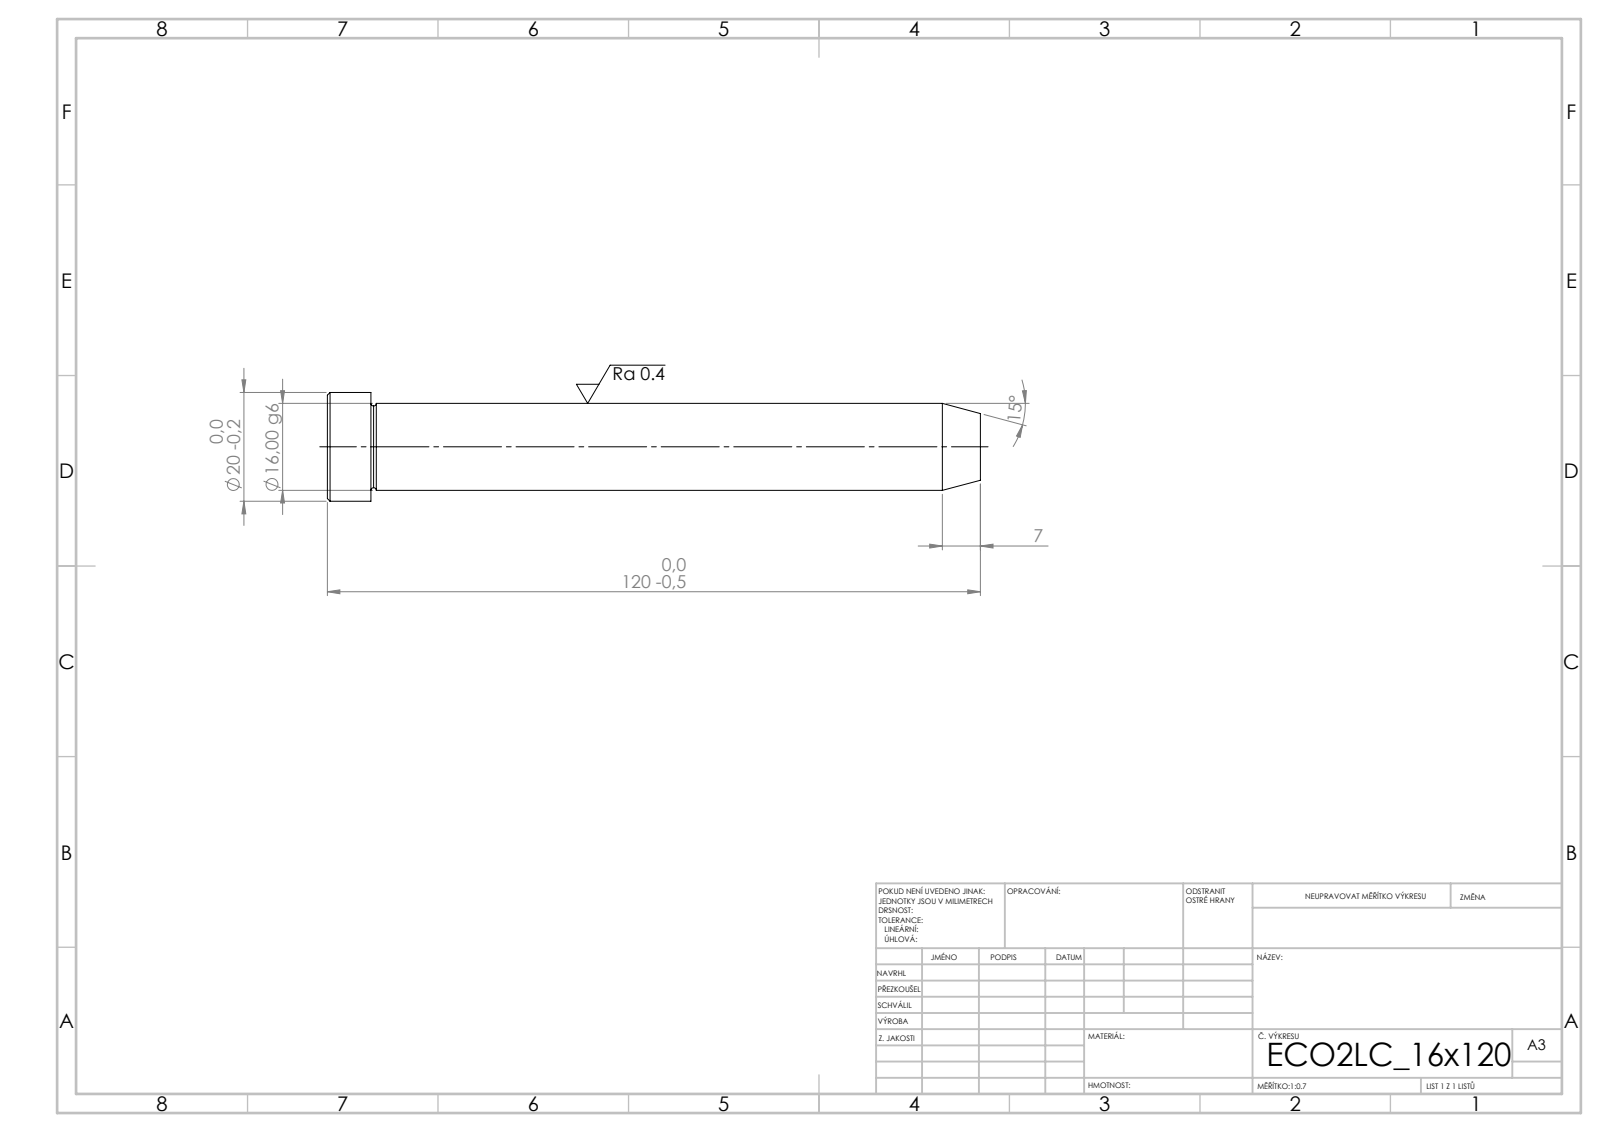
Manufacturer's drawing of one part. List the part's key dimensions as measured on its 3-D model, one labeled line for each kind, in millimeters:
STEP written by: SolidWorks 2019 (CONFIG_CONTROL_DESIGN)
Units: millimetres
Bodies: 1 solid, 15 faces (3 planar, 4 cylindrical, 8 other)
Overall size (bounding box): 120 × 20 × 20
Volume: 24 701 mm³ · Surface area: 6 654 mm²
Round bosses / shafts (diameter × count): ⌀20 ×1, ⌀16 ×1
Main face-to-face distances: 120, 112, 8
